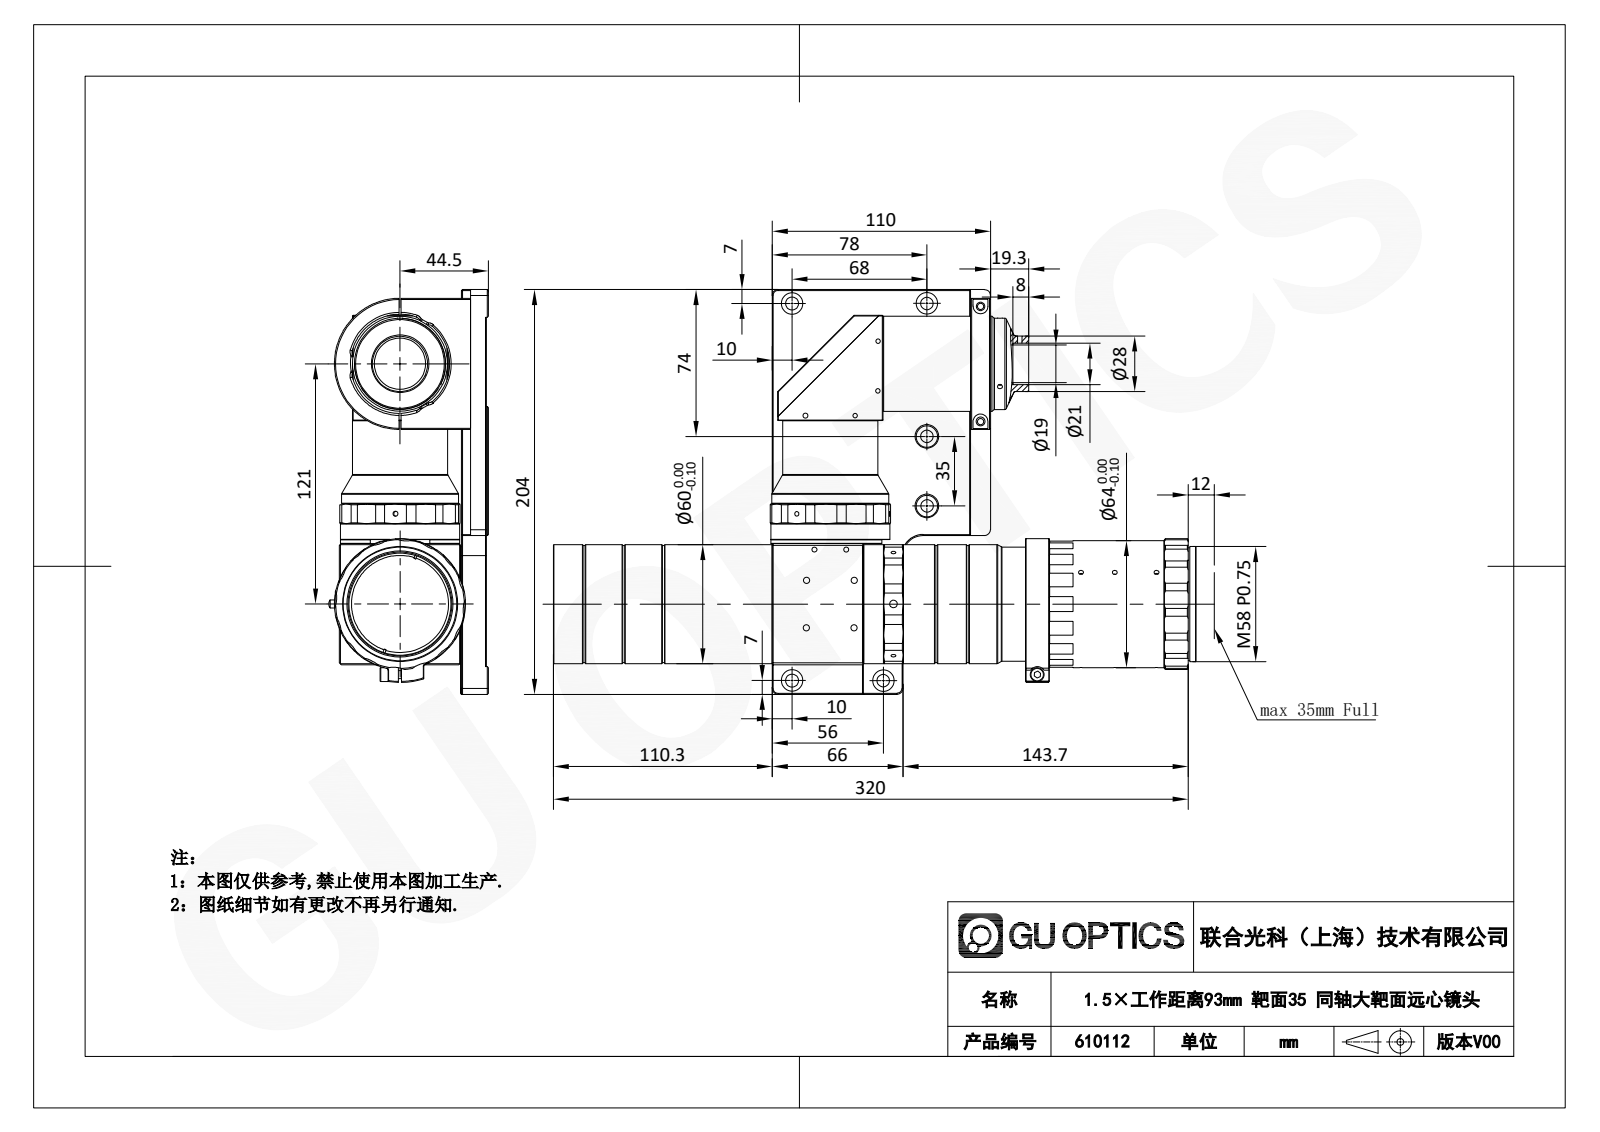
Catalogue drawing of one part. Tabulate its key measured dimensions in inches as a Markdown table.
| quantity | value |
| --- | --- |
| part name | DTCA35F-29.3C-G-M58-AL(21) |
| STEP written by | SolidWorks 2017 (CONFIG_CONTROL_DESIGN) |
| units | inches |
| bodies | 1 solid, 1349 faces (382 planar, 492 cylindrical, 475 other) |
| overall size | 12.754 × 8.031 × 3.16 |
| volume | 93.37 in³ |
| surface area | 296.9 in² |
| round holes (diameter × count) | 0.098 × 22, 0.13 × 15, 0.177 × 15, 0.094 × 13, 0.295 × 9, 0.256 × 6, 0.433 × 6, 0.126 × 4, 0.236 × 4, 0.087 × 2, 0.059 × 1, 0.134 × 1 |
| round bosses / shafts (diameter × count) | 2.362 × 2, 2.323 × 2, 1.89 × 2, 0.157 × 2, 2.598 × 1, 2.52 × 1, 2.441 × 1, 2.402 × 1 |
| partial cylindrical surfaces (radius × count) | 0.591 × 32, 0.118 × 11, 0.079 × 10, 0.059 × 3, 0.02 × 2, 0.039 × 2, 0.148 × 2, 0.061 × 1 |
| main face-to-face distances | 0.492, 0.039, 0.531, 2.913, 2.657, 4.331, 2.953, 2.421, 7.307, 2.976 |
| hole center spacings | 0.945, 1.575, 1.63, 0.028, 0.197, 0.668, 1.336, 1.63 |
